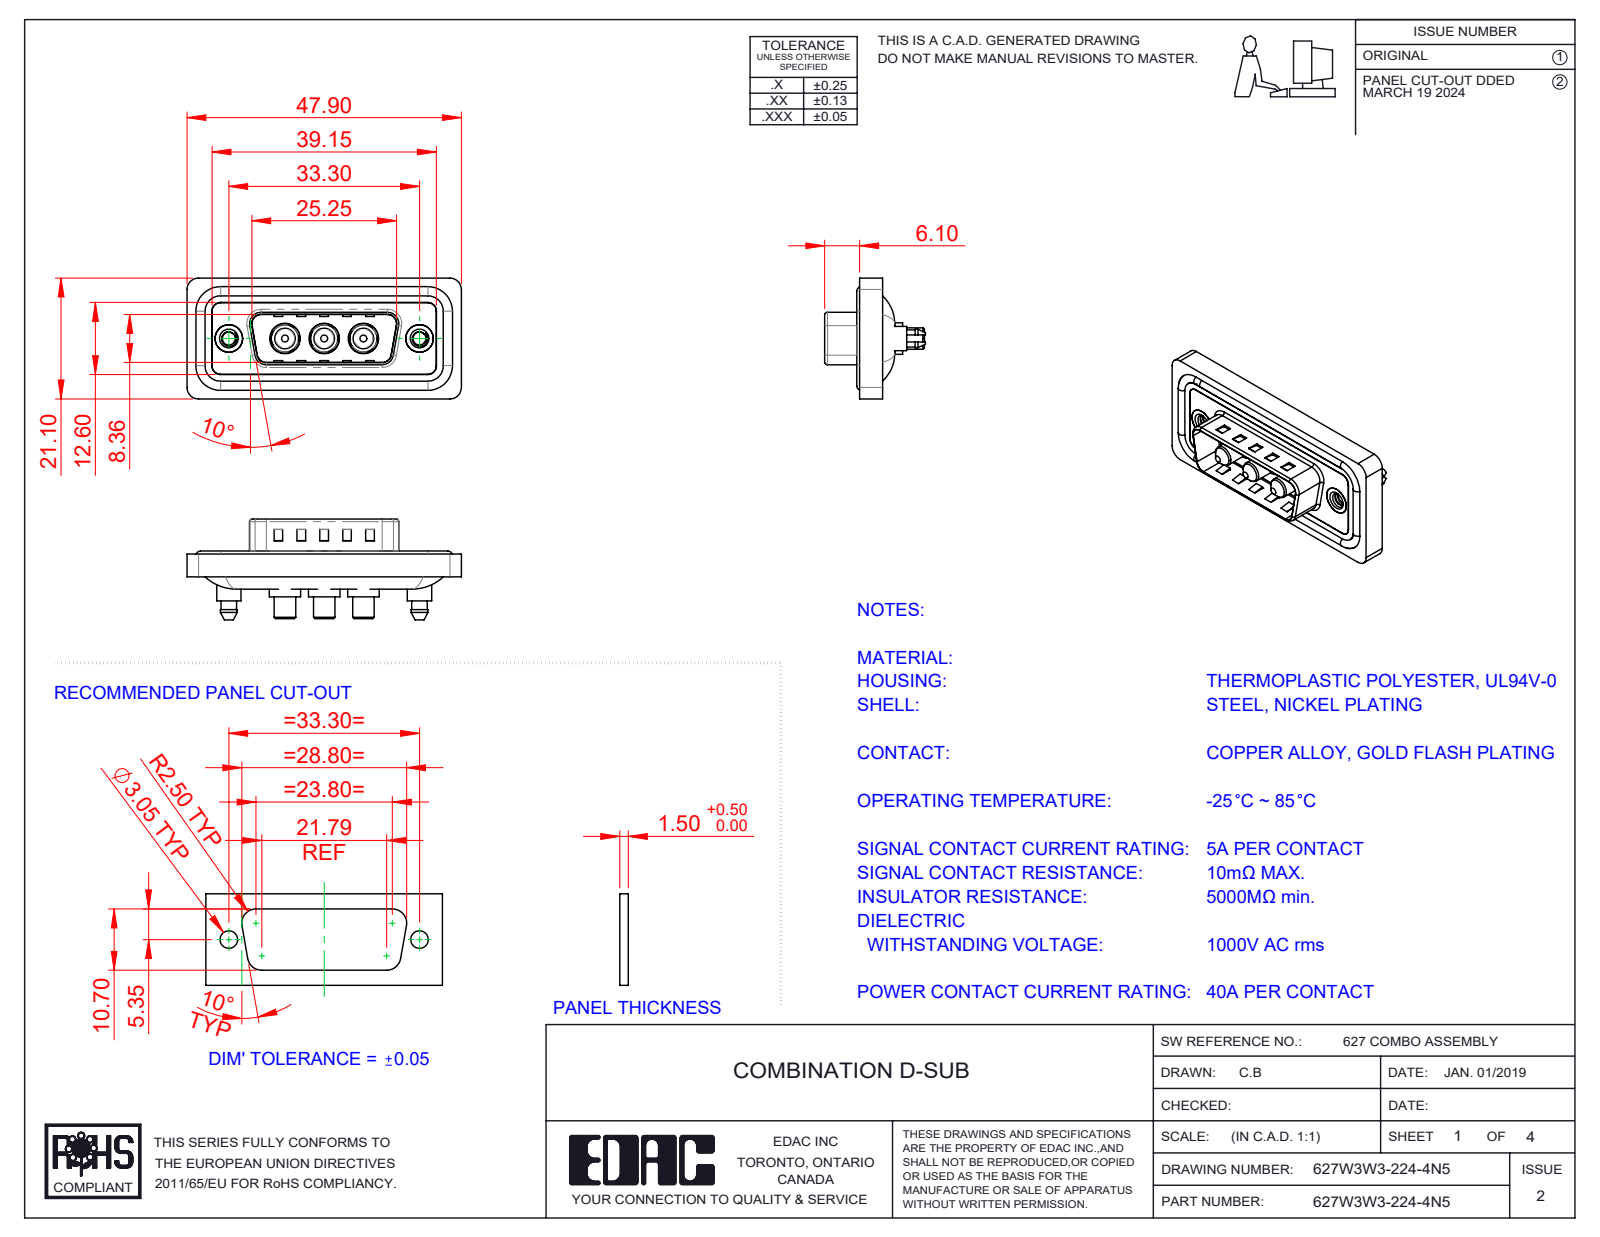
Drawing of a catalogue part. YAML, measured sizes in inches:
part_name: "627Combo Threaded Boardlock_5; 627Combo Shell Rear_15 Contacts; 627Combo Housing_3W3; 627Combo Shell Front_15 Contacts (+3 more)"
step_written_by: "SolidWorks 2023 (CONFIG_CONTROL_DESIGN)"
units: inches
bodies: {solids: 13, faces: 614, planar: 223, cylindrical: 273, other: 118}
overall_size: [1.886, 0.831, 0.693]
volume: 0.352
surface_area: 14.13
round_holes:
  - {diameter: 0.191, count: 3}
  - {diameter: 0.209, count: 3}
  - {diameter: 0.089, count: 2}
  - {diameter: 0.157, count: 2}
  - {diameter: 0.189, count: 2}
  - {diameter: 0.197, count: 2}
round_bosses_or_shafts:
  - {diameter: 0.063, count: 4}
  - {diameter: 0.217, count: 3}
  - {diameter: 0.205, count: 3}
  - {diameter: 0.187, count: 3}
  - {diameter: 0.148, count: 3}
  - {diameter: 0.142, count: 3}
  - {diameter: 0.213, count: 2}
  - {diameter: 0.193, count: 2}
partial_cylinders:
  - {radius: 0.059, count: 28}
  - {radius: 0.079, count: 20}
  - {radius: 0.063, count: 10}
  - {radius: 0.02, count: 8}
  - {radius: 0.01, count: 4}
  - {radius: 0.024, count: 4}
  - {radius: 0.026, count: 4}
  - {radius: 0.035, count: 4}
face_to_face_distances: [0.016, 0.043, 0.122, 0.059, 0.063, 0.02, 0.114, 0.157, 0.028, 0.032]
hole_center_spacings: [0.27, 0.386, 0.656, 0.925, 0.539, 1.311]
